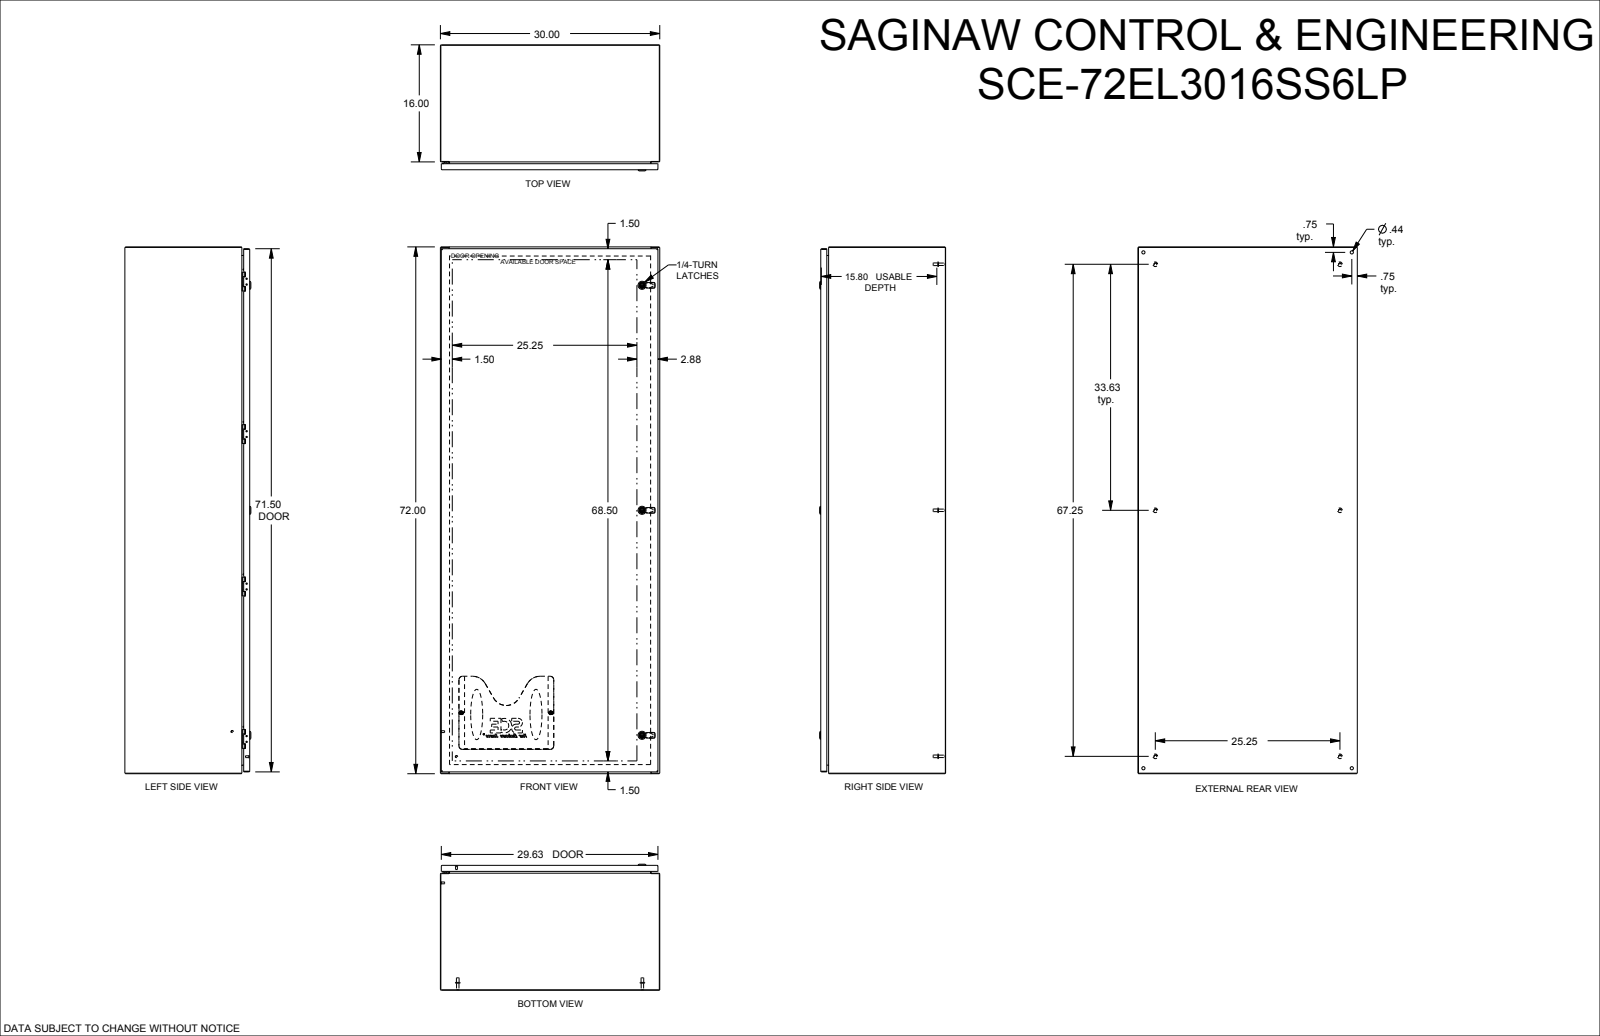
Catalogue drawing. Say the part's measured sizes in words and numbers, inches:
The part is named "SCE-72EL3016SS6LP". Its 3-D file was written by "SolidWorks 2019 (CONFIG_CONTROL_DESIGN)". It is 0 solids with 3644 faces: 2284 planar, 923 cylindrical and 437 other. Overall it measures 72 by 30 by 17.23 inches. Round holes: 8 of diameter 0.158, 8 of diameter 0.166, 8 of diameter 0.172, 8 of diameter 0.203, 8 of diameter 0.21, 4 of diameter 0.437, 3 of diameter 0.197, 3 of diameter 0.315, 3 of diameter 0.394, 3 of diameter 0.634, 2 of diameter 0.25, 1 of diameter 0.2. Round bosses or shafts: 8 of diameter 0.17, 6 of diameter 0.366, 6 of diameter 0.332, 5 of diameter 0.196, 4 of diameter 0.248, 3 of diameter 1.102, 3 of diameter 0.866, 3 of diameter 0.802. Partial cylindrical surfaces (rounded edges, fillets, slot ends): 82 of radius 0.012, 36 of radius 0.063, 28 of radius 0.02, 26 of radius 0.01, 17 of radius 0.015, 17 of radius 0.045, 13 of radius 0.07, 13 of radius 0.145. The main face-to-face distances are 0.075, 29.925, 0.075, 16.998, 16.923, 17.073, 16.998, 29.85, 30, 71.925. The hole center spacings are 20.833, 20.833, 41.667, 20.046, 41.667, 62.5, 0.787, 0.787.
